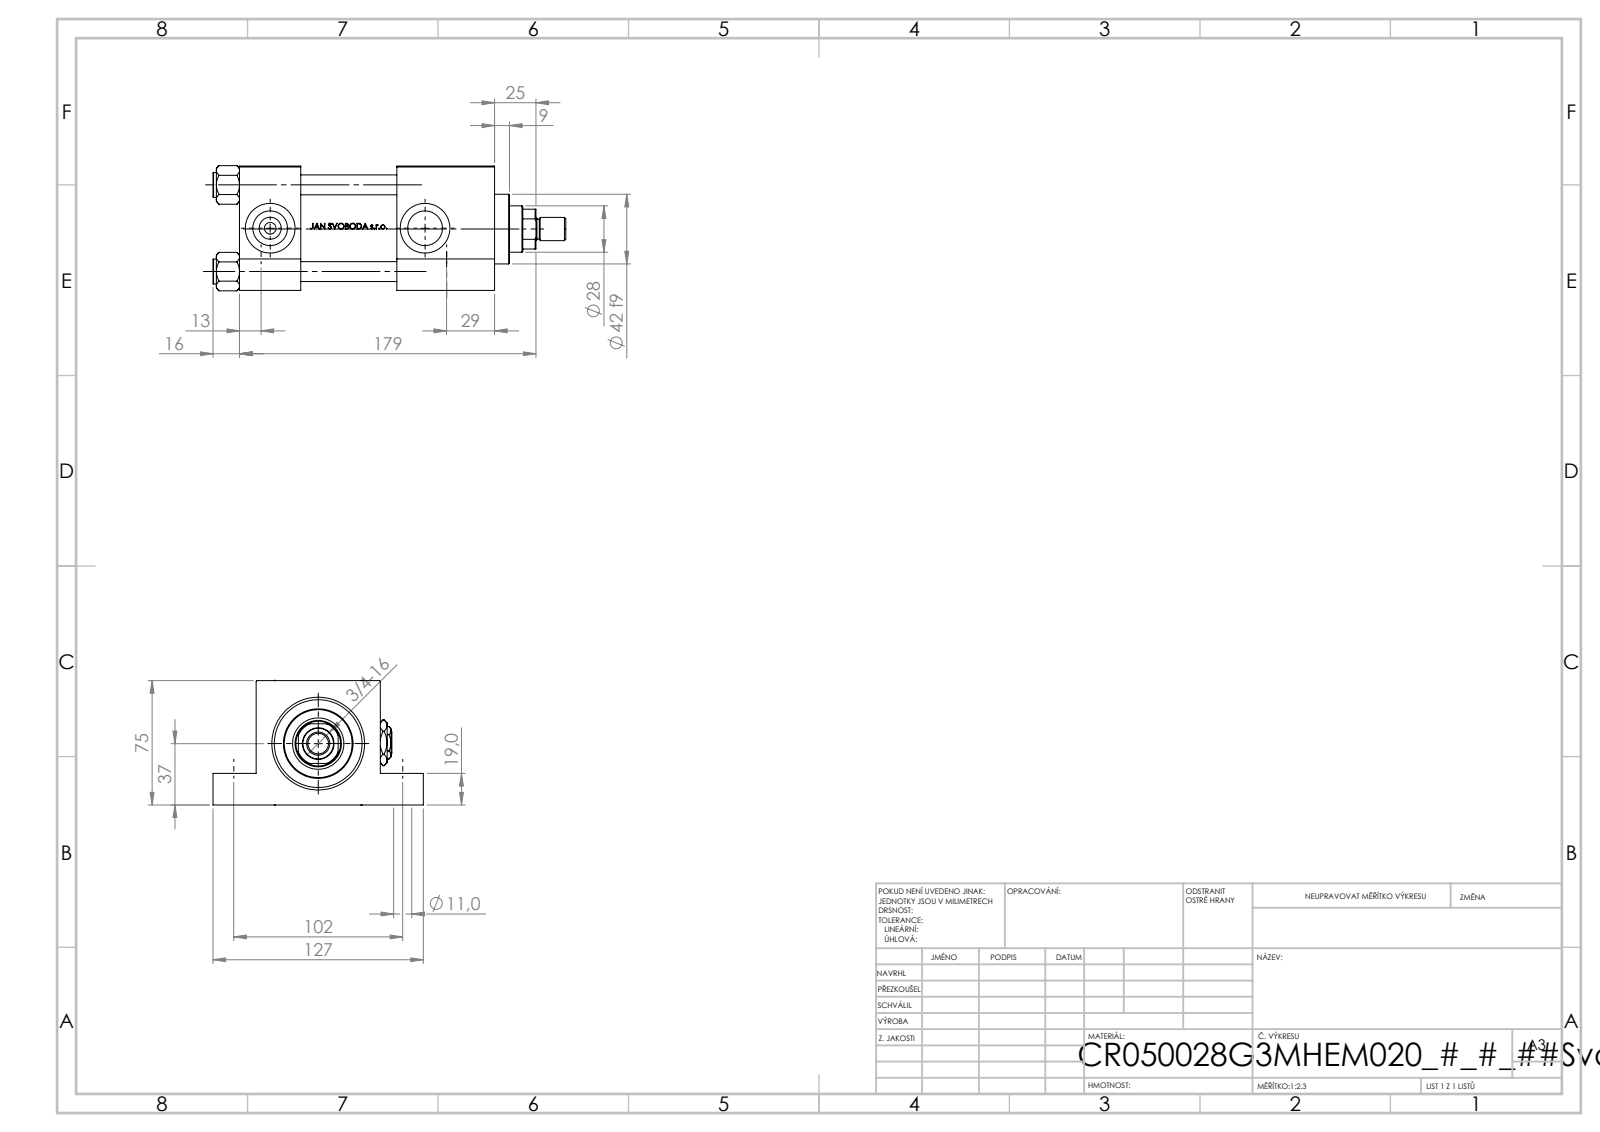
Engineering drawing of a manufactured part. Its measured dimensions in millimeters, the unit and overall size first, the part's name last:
Units: millimetres
Overall size (bounding box): 213 × 127 × 75.54
Round holes (diameter × count): ⌀12 ×4, ⌀11 ×3, ⌀7 ×2, ⌀20.96 ×2, ⌀30 ×2, ⌀11 ×1, ⌀18.5 ×1, ⌀28 ×1, ⌀31 ×1, ⌀41 ×1, ⌀50 ×1, ⌀53 ×1
Round bosses / shafts (diameter × count): ⌀15 ×4, ⌀56 ×1, ⌀42 ×1, ⌀14 ×1, ⌀12 ×1
Partial cylindrical surfaces — rounded edges, fillets, slot ends (radius × count): R13.5 ×1
Main face-to-face distances: 75, 37, 154, 117, 19, 56, 95, 58, 59, 26
Hole centre spacings: 52.3, 36.63, 37.34, 73.96, 102, 112, 151.49, 93.5
Volume: 765 016 mm³ · Surface area: 168 689 mm²
Bodies: 14 solids, 1197 faces (481 planar, 136 cylindrical, 580 other)
Part name (STEP PRODUCT): Zatka_pro_OIL_PORT; V215_VC_A; V215CR_G_TYCINKA; NUT_M5_G (+3 more)
STEP written by: SolidWorks 2019 (CONFIG_CONTROL_DESIGN)
